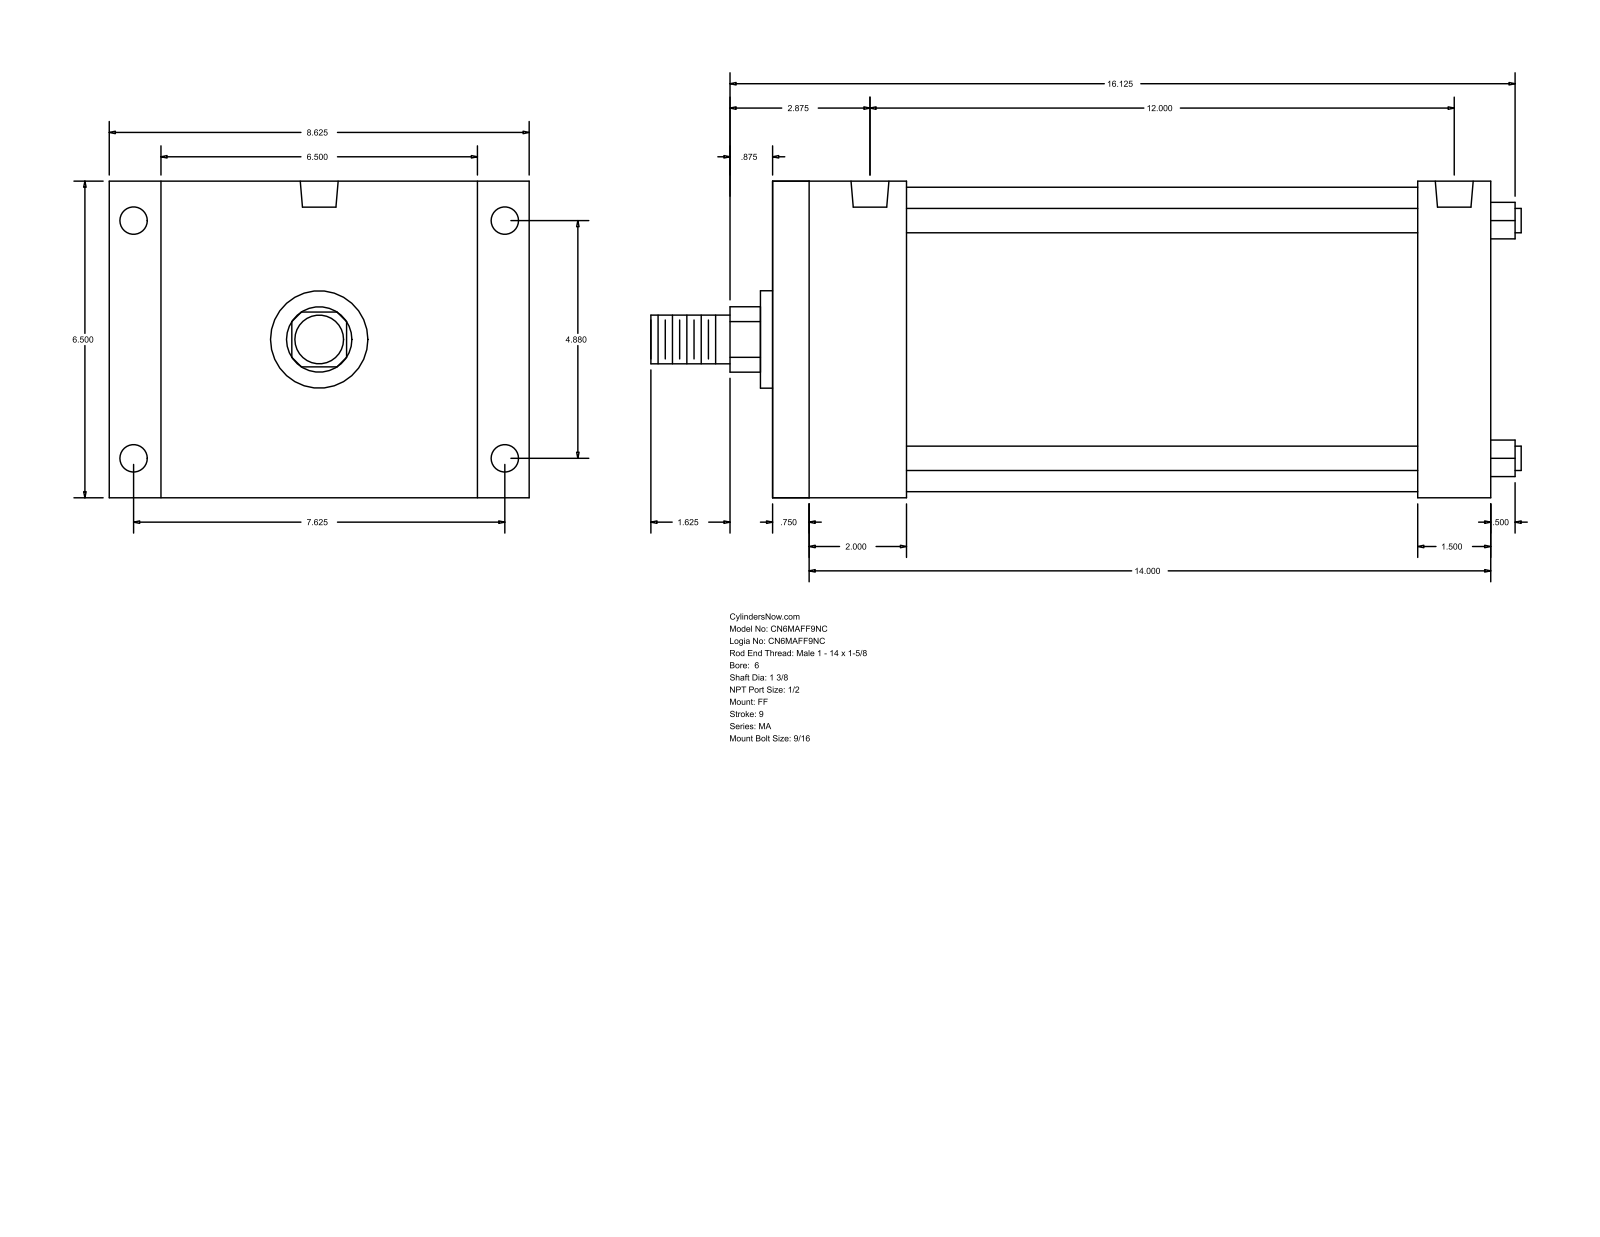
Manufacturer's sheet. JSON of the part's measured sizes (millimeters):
{"part_name": "MA_FF__0600_1.375", "step_written_by": "GSSL Pune (CONFIG_CONTROL_DESIGN)", "units": "millimeters", "bodies": {"solids": 0, "faces": 92, "planar": 64, "cylindrical": 28, "other": 0}, "overall_size": [454.02, 219.07, 165.1], "round_holes": [[14.29, 4], [17.46, 4], [19.77, 2]], "round_bosses_or_shafts": [[12.7, 4], [158.75, 1], [50.8, 1], [34.92, 1], [25.4, 1]], "partial_cylinders_radius": [[17.06, 1]], "face_to_face_distances": [165.1, 374.65, 15.87, 358.78, 50.8, 320.67, 66.67, 307.98, 336.54, 269.87], "hole_center_spacings": [123.96, 193.68, 229.95, 307.97, 3.18, 304.79]}
